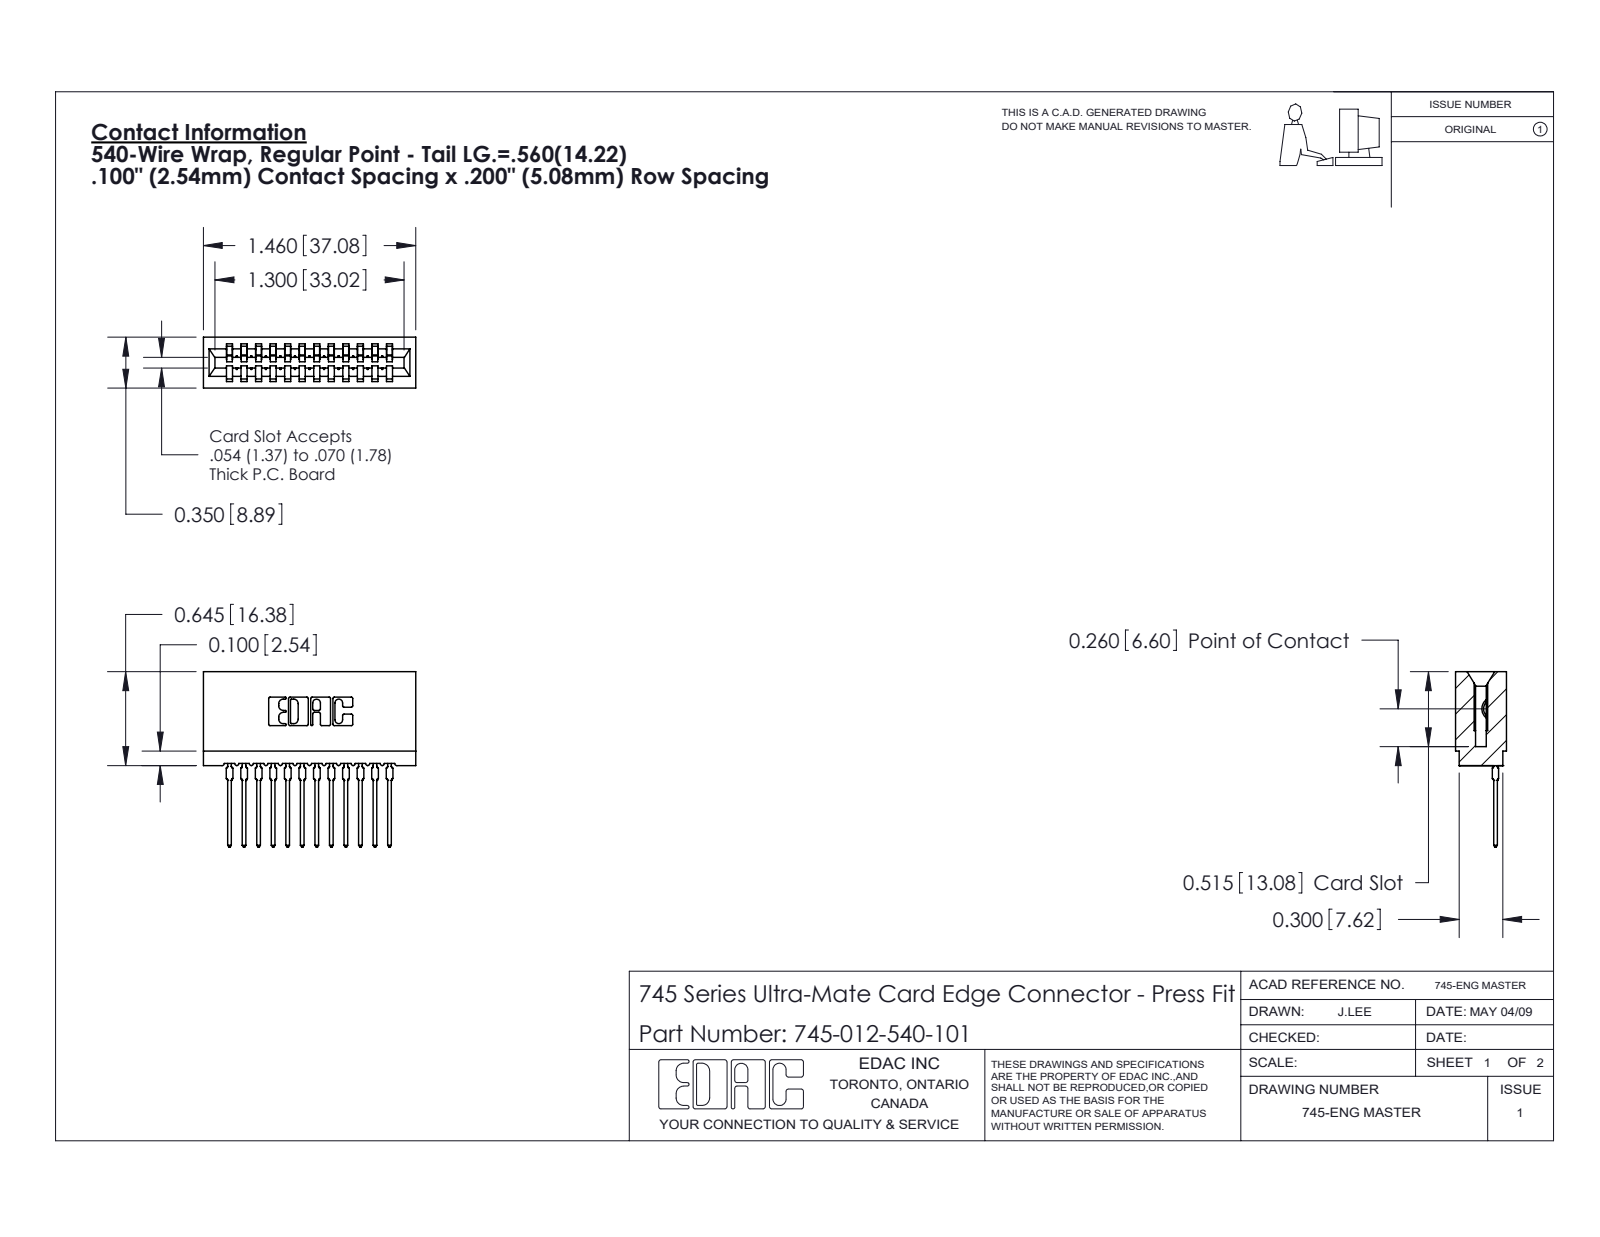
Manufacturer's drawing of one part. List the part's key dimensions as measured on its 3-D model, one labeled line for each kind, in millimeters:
Part name (STEP PRODUCT): 745-292-001_540; 745-012-540-101; 745 Part_Insulator Option - 01
STEP written by: SolidWorks 2020 (CONFIG_CONTROL_DESIGN)
Units: millimetres
Bodies: 13 solids, 1439 faces (859 planar, 268 cylindrical, 312 other)
Overall size (bounding box): 37.1 × 30.6 × 8.9
Volume: 3 440 mm³ · Surface area: 5 948 mm²
Partial cylindrical surfaces — rounded edges, fillets, slot ends (radius × count): R0.4 ×24, R0.5 ×24, R0.3 ×22, R0.2 ×6, R0.8 ×6, R0.1 ×4, R0.3 ×4, R0.7 ×3
Main face-to-face distances: 2.5, 5.1, 7.6, 12.7, 10.2, 15.2, 8.9, 1.1, 3.5, 5.4
